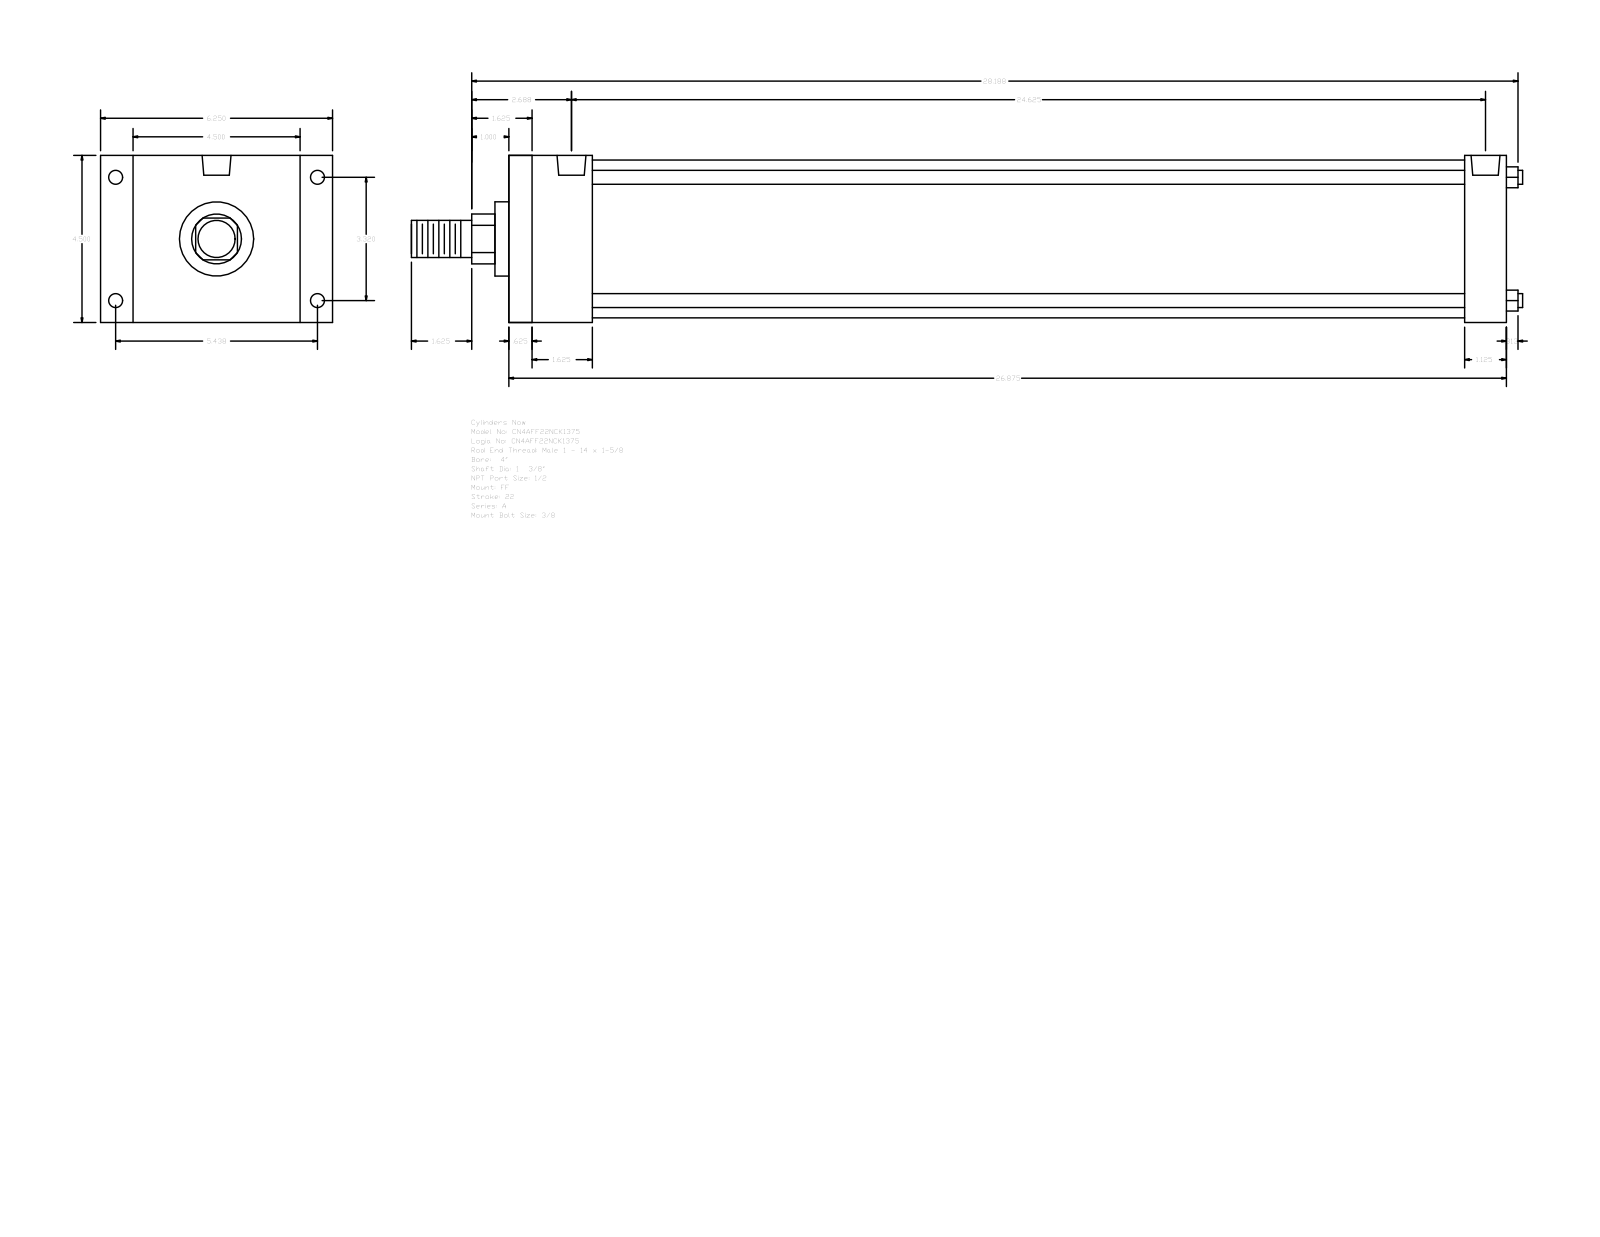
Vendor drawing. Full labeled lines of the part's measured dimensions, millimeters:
Part name (STEP PRODUCT): A_FF__0400_1.375
STEP written by: GSSL Pune (CONFIG_CONTROL_DESIGN)
Units: millimetres
Bodies: 0 solids, 92 faces (64 planar, 28 cylindrical, 0 other)
Overall size (bounding box): 760.41 × 158.75 × 114.3
Round holes (diameter × count): ⌀8.73 ×4, ⌀9.53 ×4, ⌀19.77 ×2
Round bosses / shafts (diameter × count): ⌀9.53 ×4, ⌀107.95 ×1, ⌀50.8 ×1, ⌀34.92 ×1, ⌀25.4 ×1
Partial cylindrical surfaces — rounded edges, fillets, slot ends (radius × count): R17.06 ×1
Main face-to-face distances: 114.3, 682.62, 666.75, 15.87, 57.15, 28.57, 22.23, 136.53, 654.05, 638.18
Hole centre spacings: 3.18, 84.32, 138.12, 161.82, 619.12, 622.3, 625.48
